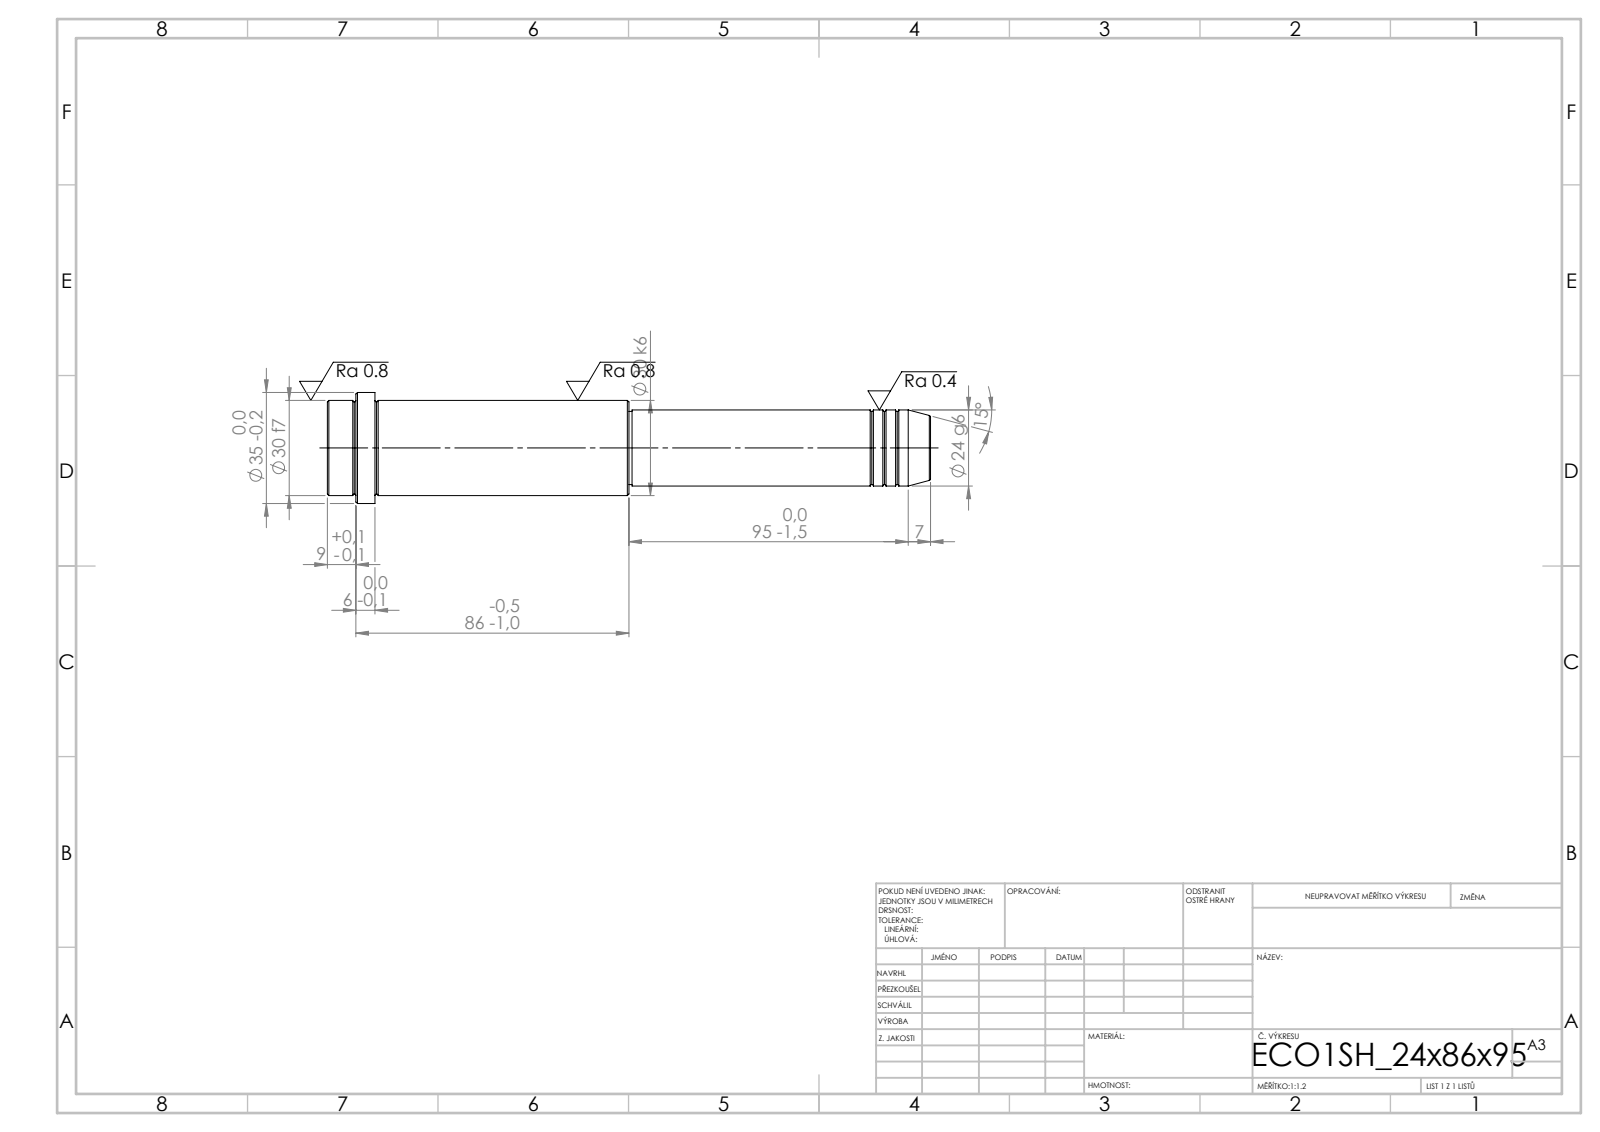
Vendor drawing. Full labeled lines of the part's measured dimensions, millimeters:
STEP written by: SolidWorks 2019 (CONFIG_CONTROL_DESIGN)
Units: millimetres
Bodies: 1 solid, 52 faces (6 planar, 16 cylindrical, 30 other)
Overall size (bounding box): 190 × 35 × 35
Volume: 110 955 mm³ · Surface area: 18 176 mm²
Round bosses / shafts (diameter × count): ⌀35 ×1, ⌀30 ×1, ⌀24 ×1, ⌀23 ×1
Main face-to-face distances: 95, 190, 175, 15, 80, 181, 86, 6, 9, 94
